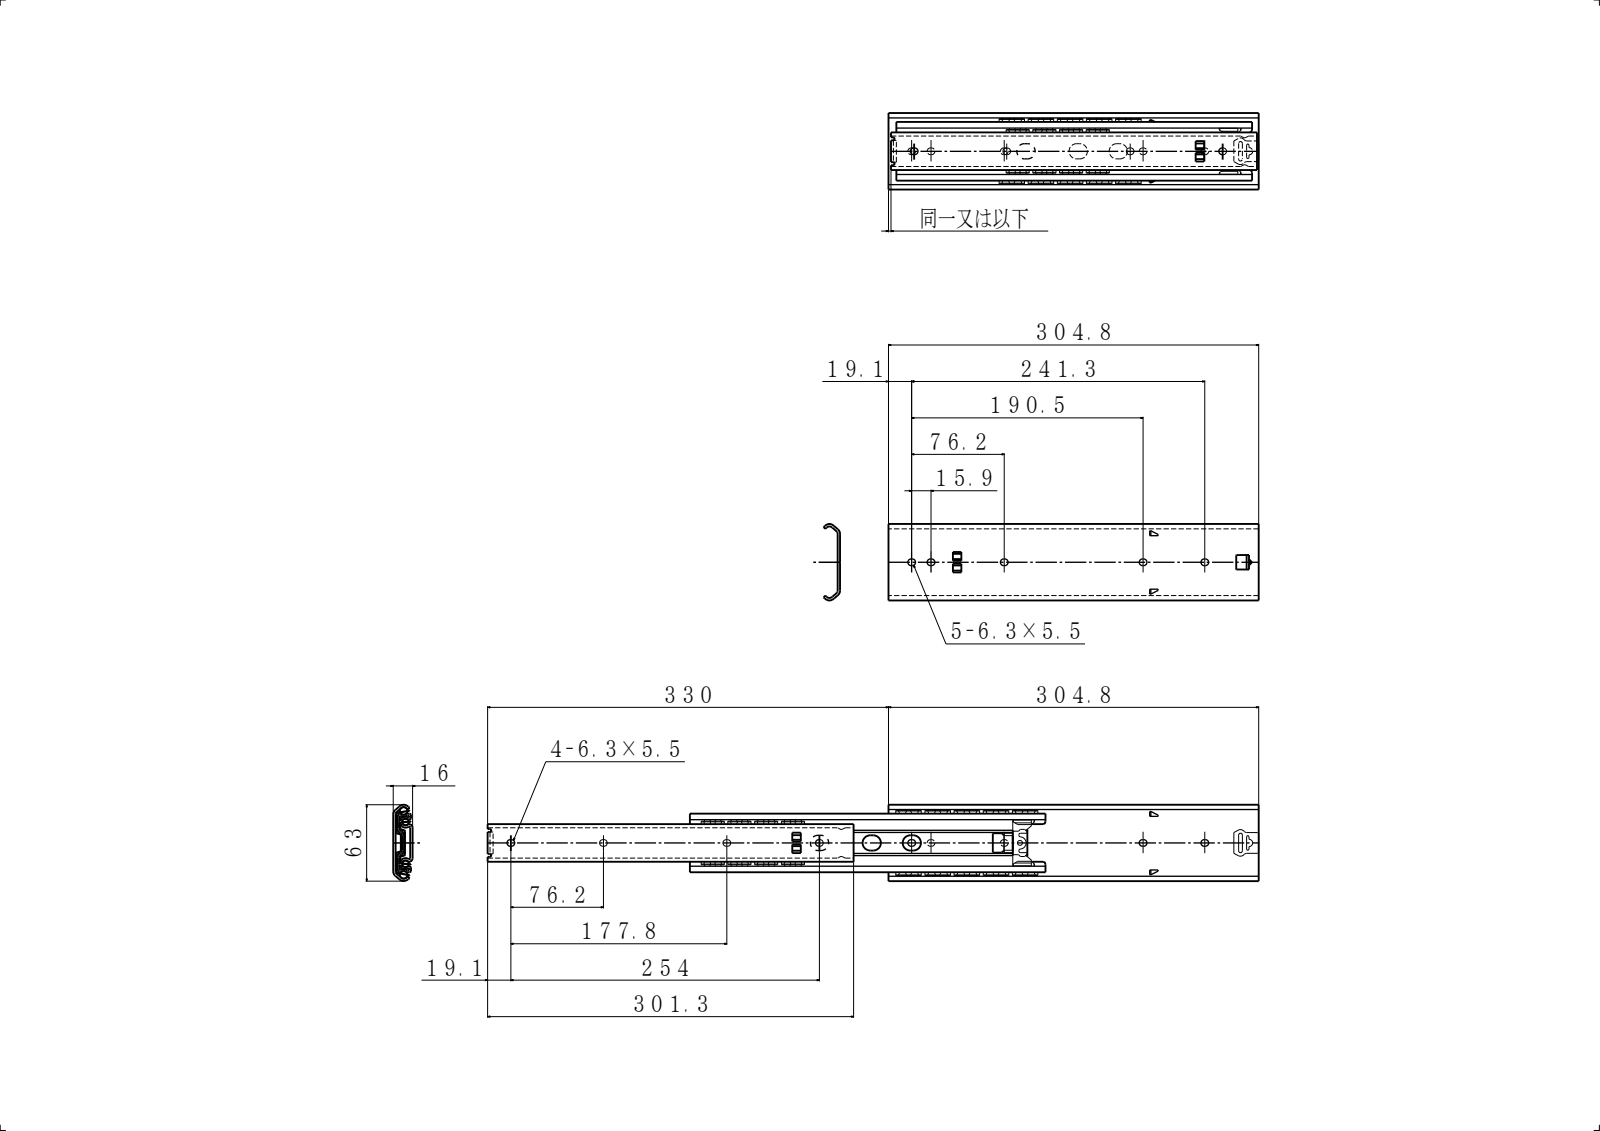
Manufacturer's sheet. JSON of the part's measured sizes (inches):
{"part_name": "C630-12 IM; PN68; PN161A; PN48B (+5 more)", "step_written_by": "SolidWorks 2019 (CONFIG_CONTROL_DESIGN)", "units": "inches", "bodies": {"solids": 10, "faces": 640, "planar": 395, "cylindrical": 243, "other": 2}, "overall_size": [25.046, 2.48, 0.63], "volume_in3": 7.499, "surface_area_in2": 216.1, "round_holes": [[0.213, 1]], "round_bosses_or_shafts": [[0.197, 1]], "partial_cylinders_radius": [[0.039, 22], [0.02, 20], [0.108, 18], [0.079, 14], [0.012, 12], [0.047, 10], [0.008, 8], [0.063, 8]], "face_to_face_distances": [0.079, 0.551, 0.061, 0.472, 0.63, 0.051, 0.5, 0.161, 0.113, 0.439]}
